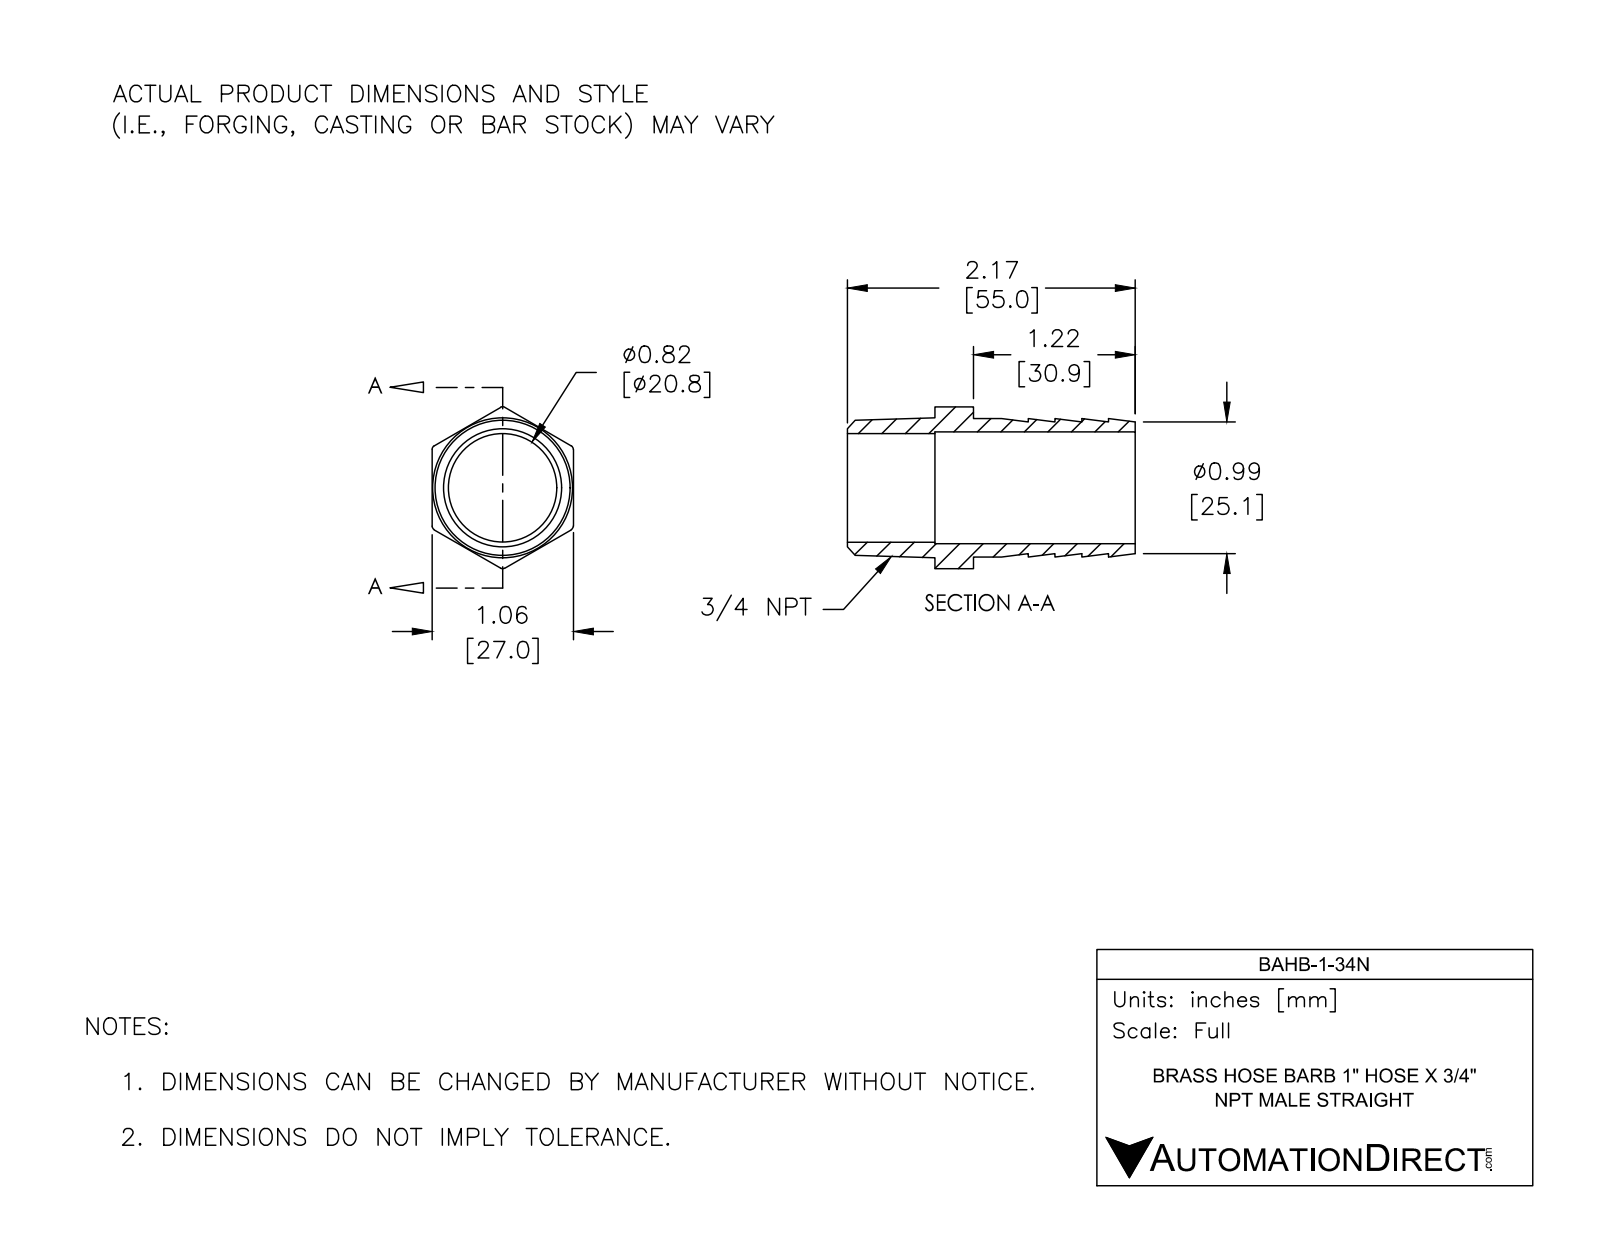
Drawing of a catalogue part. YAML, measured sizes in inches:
part_name: "BAHB-1-34N"
step_written_by: "SolidWorks 2017 (AUTOMOTIVE_DESIGN)"
units: inches
bodies: {solids: 1, faces: 41, planar: 15, cylindrical: 12, other: 14}
overall_size: [2.166, 1.218, 1.063]
volume: 0.646
surface_area: 13.78
round_holes:
  - {diameter: 0.817, count: 1}
  - {diameter: 0.84, count: 1}
round_bosses_or_shafts:
  - {diameter: 1.043, count: 1}
partial_cylinders:
  - {radius: 0.03, count: 6}
face_to_face_distances: [1.062, 0.402, 0.201, 0.201, 1.506, 1.216, 0.29, 2.166, 0.95, 0.66]
